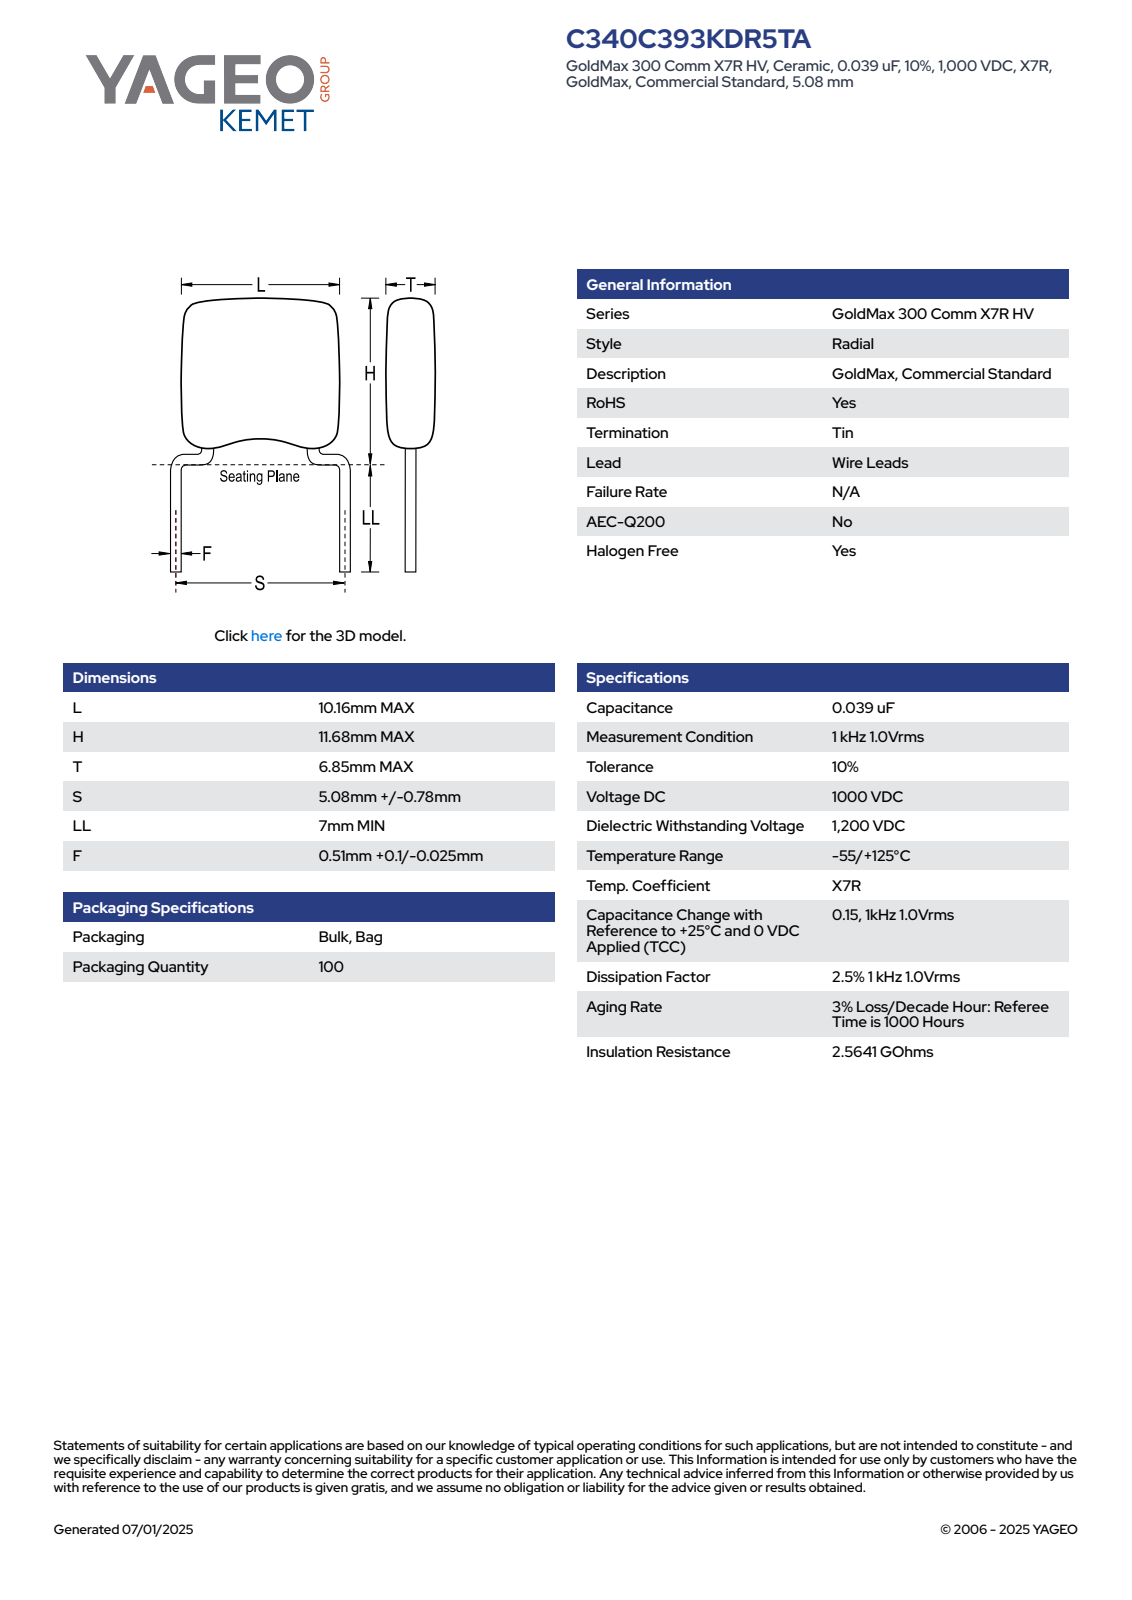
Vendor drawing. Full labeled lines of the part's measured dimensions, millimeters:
Part name (STEP PRODUCT): CCR_SB_10.16X11.68_L10.16H11.68T6.85S5.08LL7F0.51
STEP written by: SolidWorks 2014 (AUTOMOTIVE_DESIGN)
Units: millimetres
Bodies: 4 solids, 97 faces (65 planar, 14 cylindrical, 18 other)
Overall size (bounding box): 18.68 × 10.16 × 6.86
Volume: 655 mm³ · Surface area: 460 mm²
Round bosses / shafts (diameter × count): ⌀0.51 ×2
Partial cylindrical surfaces — rounded edges, fillets, slot ends (radius × count): R1 ×10
Main face-to-face distances: 6.85, 9.62, 10.16, 5.28, 4.34, 4.42, 0.86, 5.2, 0.37, 0.97
